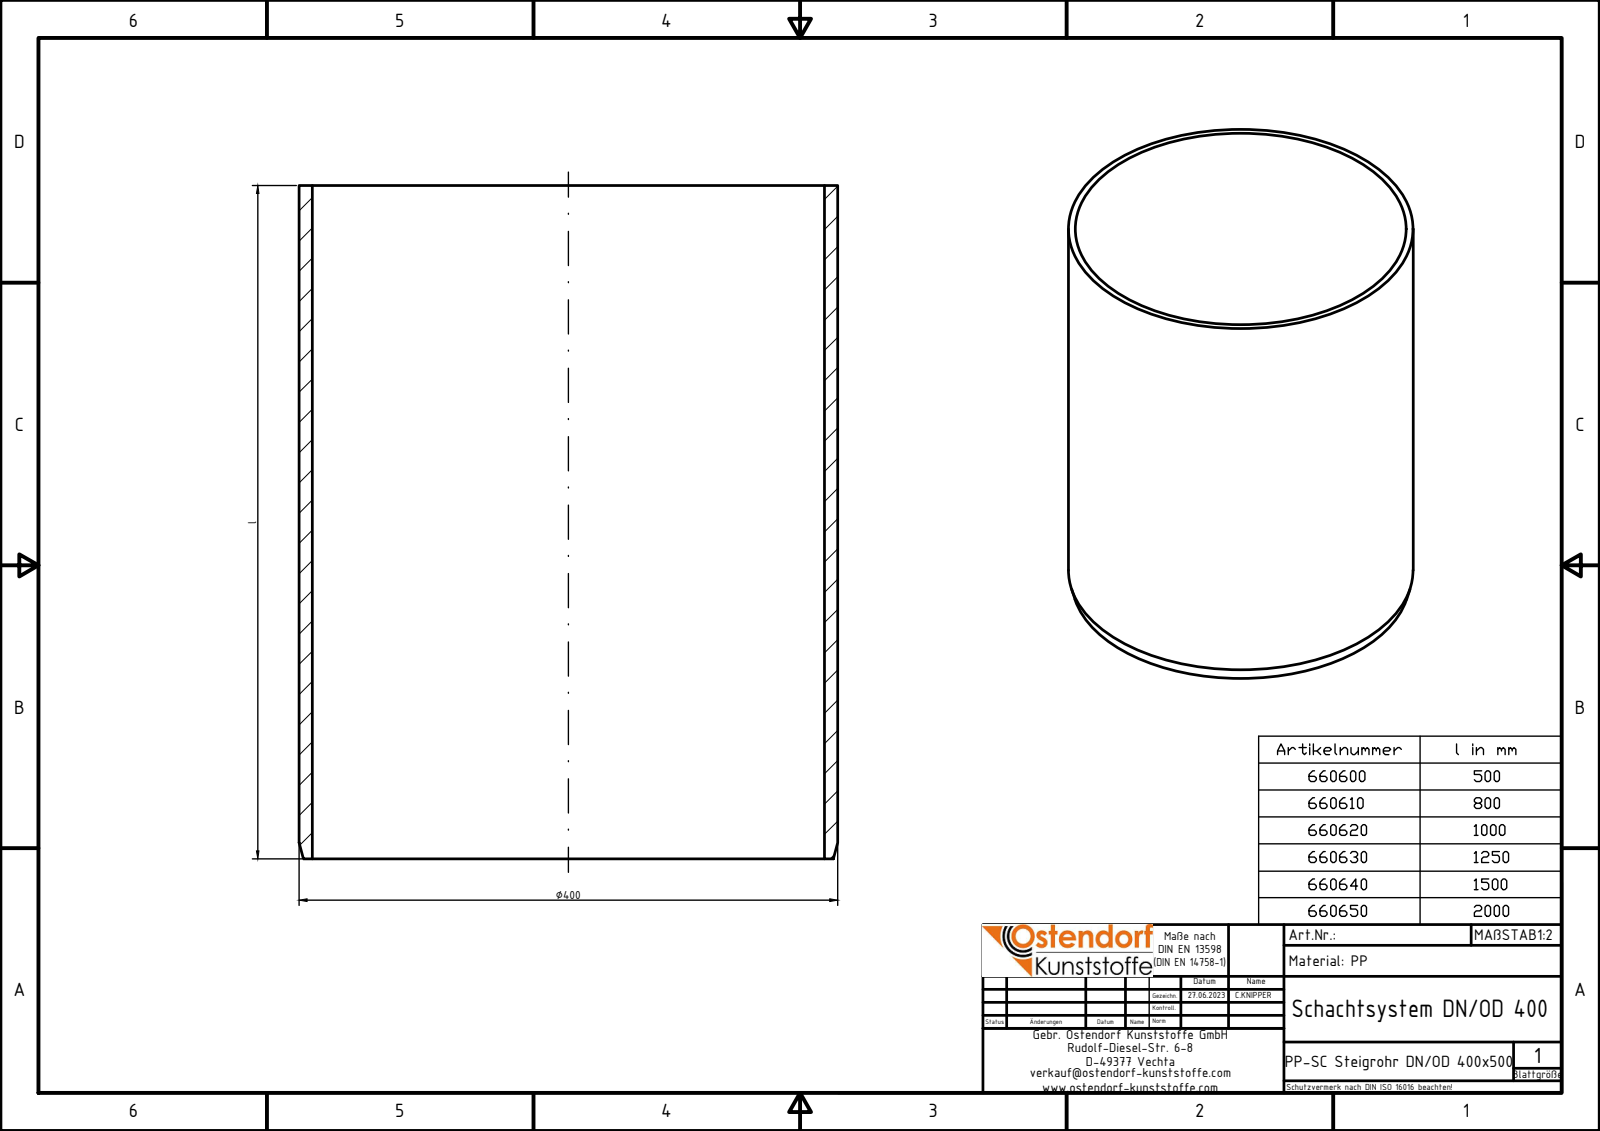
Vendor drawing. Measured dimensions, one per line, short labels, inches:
name: 660600
written by: Autodesk Inventor 2020 (AUTOMOTIVE_DESIGN)
unit: in
bodies: 1 solid, 5 faces (2 planar, 2 cylindrical, 1 other)
size: 19.685 × 15.748 × 15.748
volume: 365.1 in³; area: 1 931 in²
holes: 1× ⌀14.976
bosses: 1× ⌀15.748
face distances: 19.685
